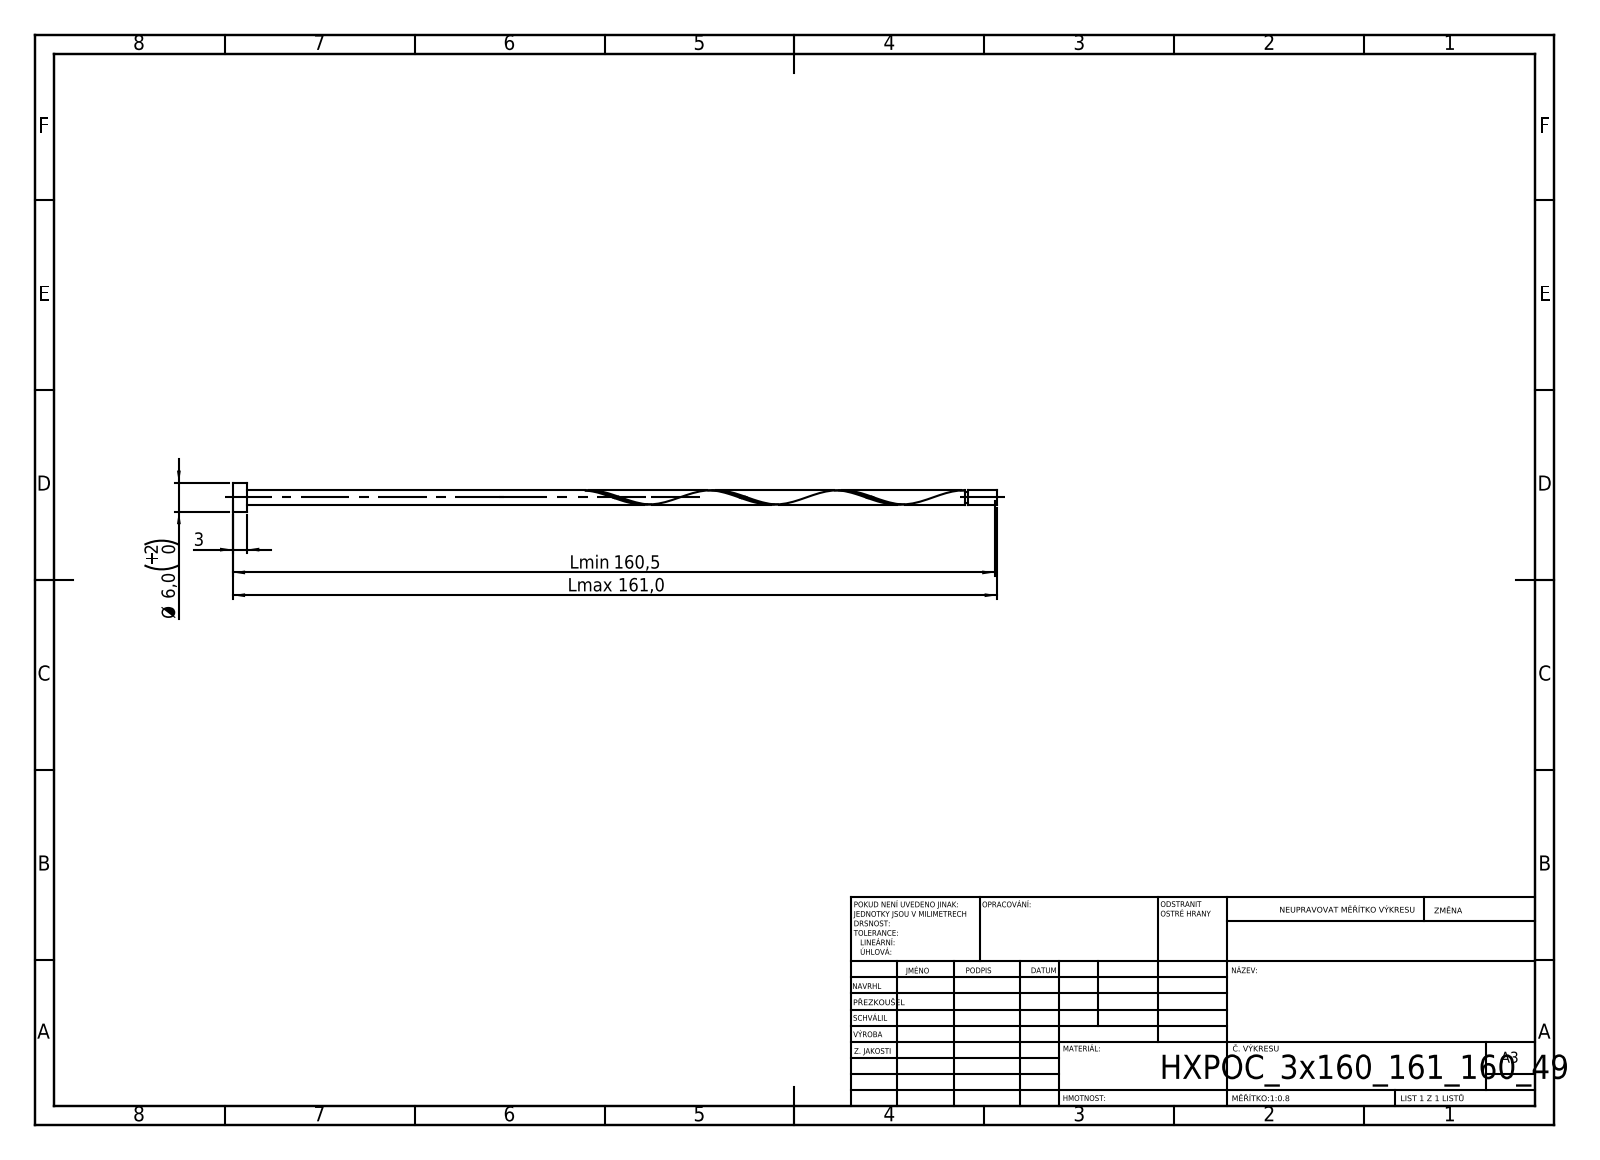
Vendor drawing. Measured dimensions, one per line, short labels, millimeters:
written by: SolidWorks 2019 (CONFIG_CONTROL_DESIGN)
unit: mm
bodies: 1 solid, 16 faces (6 planar, 9 cylindrical, 1 other)
size: 161 × 6 × 6
volume: 1 441 mm³; area: 2 133 mm²
bosses: 1× ⌀6, 1× ⌀3, 1× ⌀2.4
face distances: 3, 161, 158, 154.78, 151.78, 6.22, 154.18, 151.18, 0.6, 6.82
